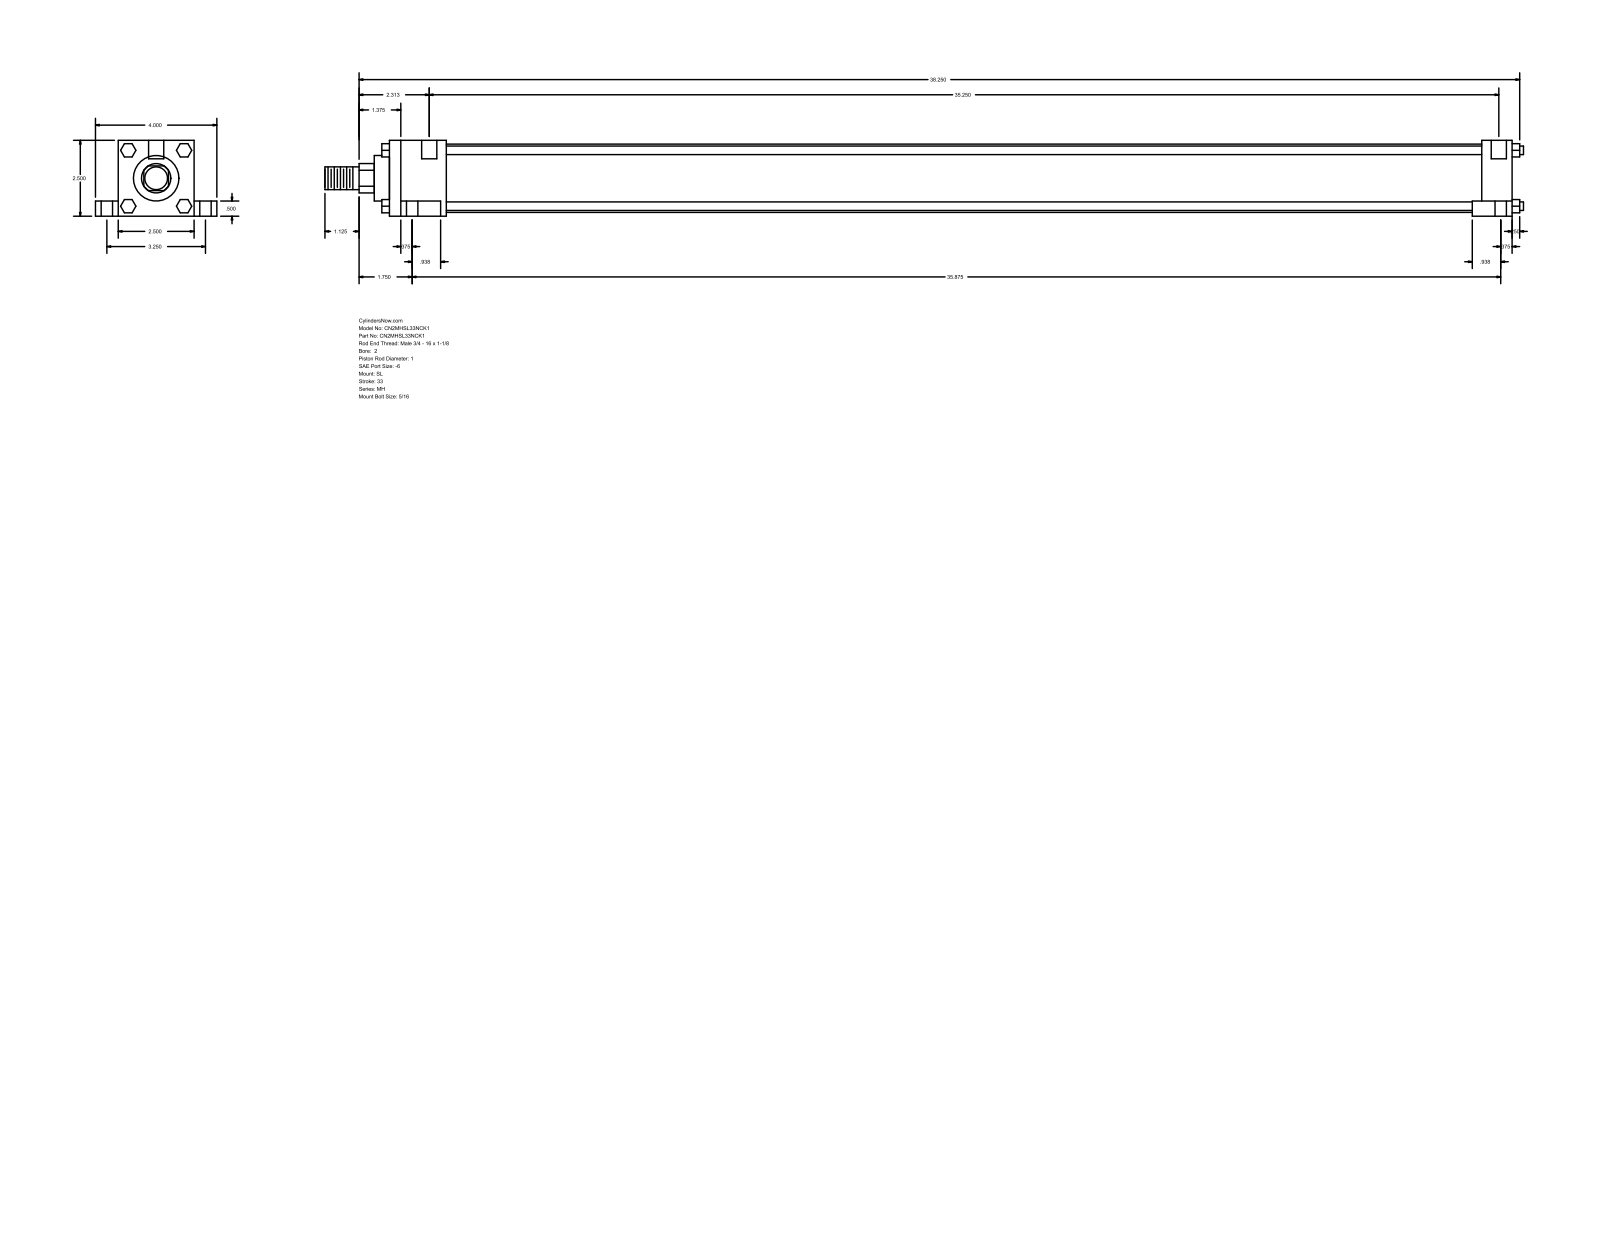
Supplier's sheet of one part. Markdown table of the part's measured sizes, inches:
| quantity | value |
| --- | --- |
| part name | MH_SL__0200_1 |
| STEP written by | GSSL Pune (CONFIG_CONTROL_DESIGN) |
| units | inches |
| bodies | 0 solids, 148 faces (112 planar, 36 cylindrical, 0 other) |
| overall size | 39.5 × 4 × 2.5 |
| round holes (diameter × count) | 0.219 × 4, 0.375 × 4, 0.625 × 4, 0.5 × 2 |
| round bosses / shafts (diameter × count) | 0.281 × 4, 2.25 × 1, 1.5 × 1, 1 × 1, 0.75 × 1 |
| partial cylindrical surfaces (radius × count) | 0.484 × 1 |
| main face-to-face distances | 2.5, 37, 0.5, 0.75, 2, 3.25, 1, 36, 1.875, 34.125 |
| hole center spacings | 1.626, 1.668, 1.719, 3.25, 35.35, 35.537, 35.562, 35.85 |
